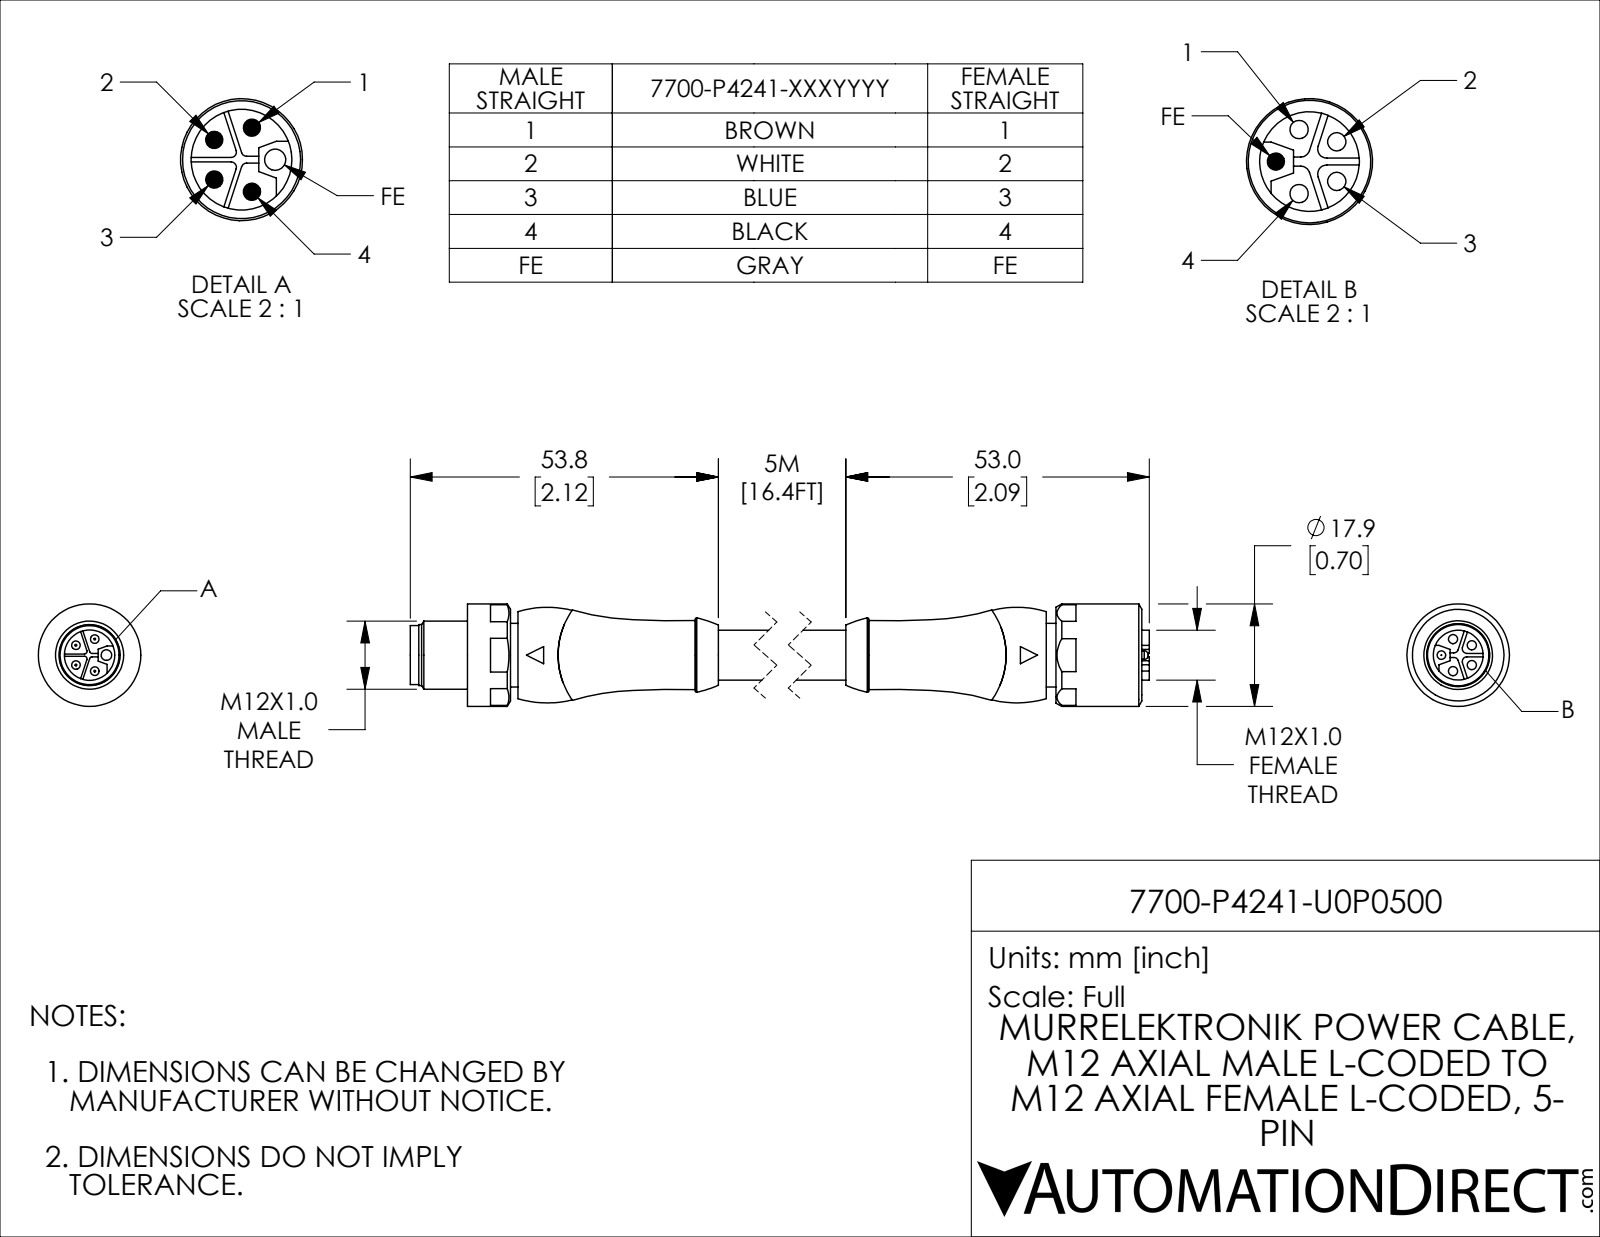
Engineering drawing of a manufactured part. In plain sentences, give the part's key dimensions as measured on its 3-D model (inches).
The part is named "7700-P4241-U0P0500; 7700-P4241-U0P0500_2; 7700-P4241-U0P0500_1". Its 3-D file was written by "SolidWorks 2021 (CONFIG_CONTROL_DESIGN)". It is 3 solids with 214 faces: 98 planar, 62 cylindrical and 54 other. Overall it measures 5.386 by 0.705 by 0.705 inches. Its volume is 1.09 cubic inches and its surface area 14.44 square inches. Round holes: 4 of diameter 0.063, 1 of diameter 0.073, 1 of diameter 0.346, 1 of diameter 0.433, 1 of diameter 0.512. Round bosses or shafts: 5 of diameter 0.059, 1 of diameter 0.705, 1 of diameter 0.51, 1 of diameter 0.469, 1 of diameter 0.437, 1 of diameter 0.419, 1 of diameter 0.406, 1 of diameter 0.343. Partial cylindrical surfaces (rounded edges, fillets, slot ends): 4 of radius 0.018, 4 of radius 0.031. The main face-to-face distances are 4.283, 0.067, 0.346, 0.666, 0.051, 0.295, 0.228, 4.941, 0.657, 4.35. The hole center spacings are 0.116, 0.136, 0.22, 0.22.
